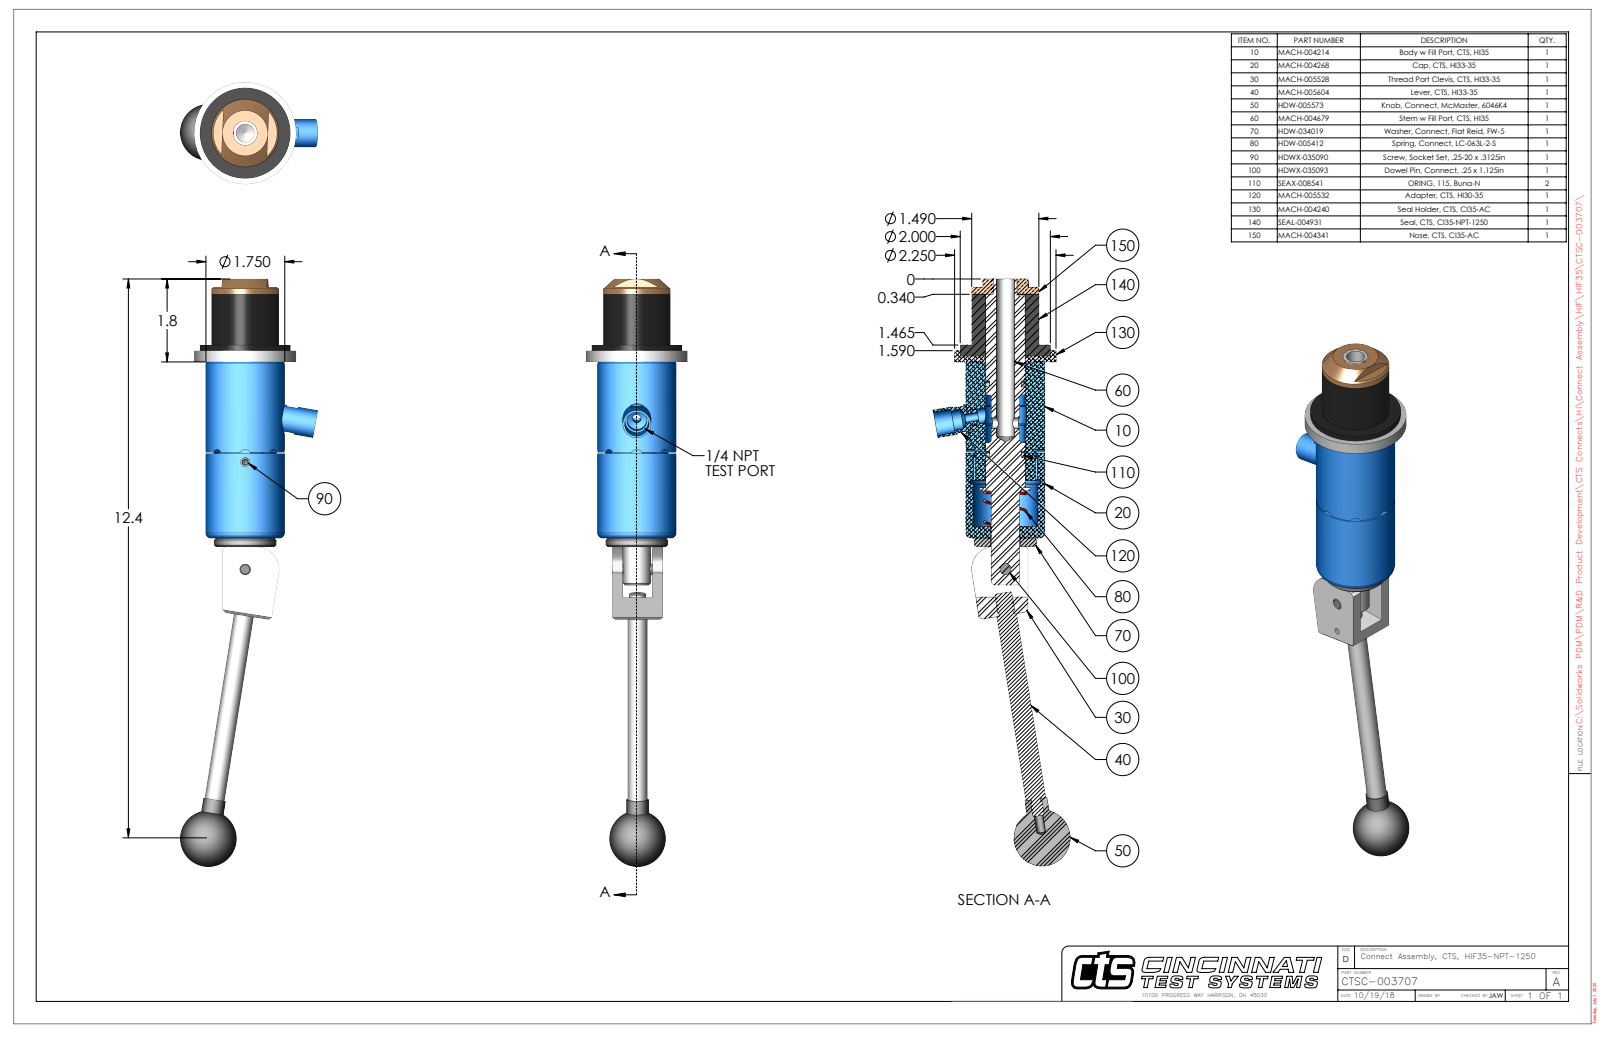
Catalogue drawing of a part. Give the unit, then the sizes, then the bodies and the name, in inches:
Units: inches
Overall size (bounding box): 13.02 × 3.043 × 2.25
Round holes (diameter × count): ⌀0.201 ×2, ⌀0.15 ×1, ⌀0.187 ×1, ⌀0.249 ×1, ⌀0.25 ×1, ⌀0.251 ×1, ⌀0.313 ×1, ⌀0.406 ×1, ⌀0.438 ×1, ⌀0.531 ×1, ⌀0.635 ×1, ⌀0.656 ×1
Round bosses / shafts (diameter × count): ⌀0.25 ×2, ⌀2.25 ×1, ⌀2 ×1, ⌀1.75 ×1, ⌀1.49 ×1, ⌀1.38 ×1, ⌀0.869 ×1, ⌀0.625 ×1
Partial cylindrical surfaces — rounded edges, fillets, slot ends (radius × count): R0.125 ×4, R0.029 ×2, R0.166 ×1, R0.166 ×1, R0.248 ×1, R0.33 ×1, R0.5 ×1, R0.695 ×1
Main face-to-face distances: 0.125, 1.375, 1.5, 5.405, 4.03, 3.905, 0.25, 1.12, 0.375, 1.125
Hole centre spacings: 0.74, 2.376, 3.116
Volume: 16.13 in³ · Surface area: 101.2 in²
Bodies: 9 solids, 285 faces (105 planar, 122 cylindrical, 58 other)
Part name (STEP PRODUCT): CTSC-003707
STEP written by: SolidWorks 2023 (AUTOMOTIVE_DESIGN)
